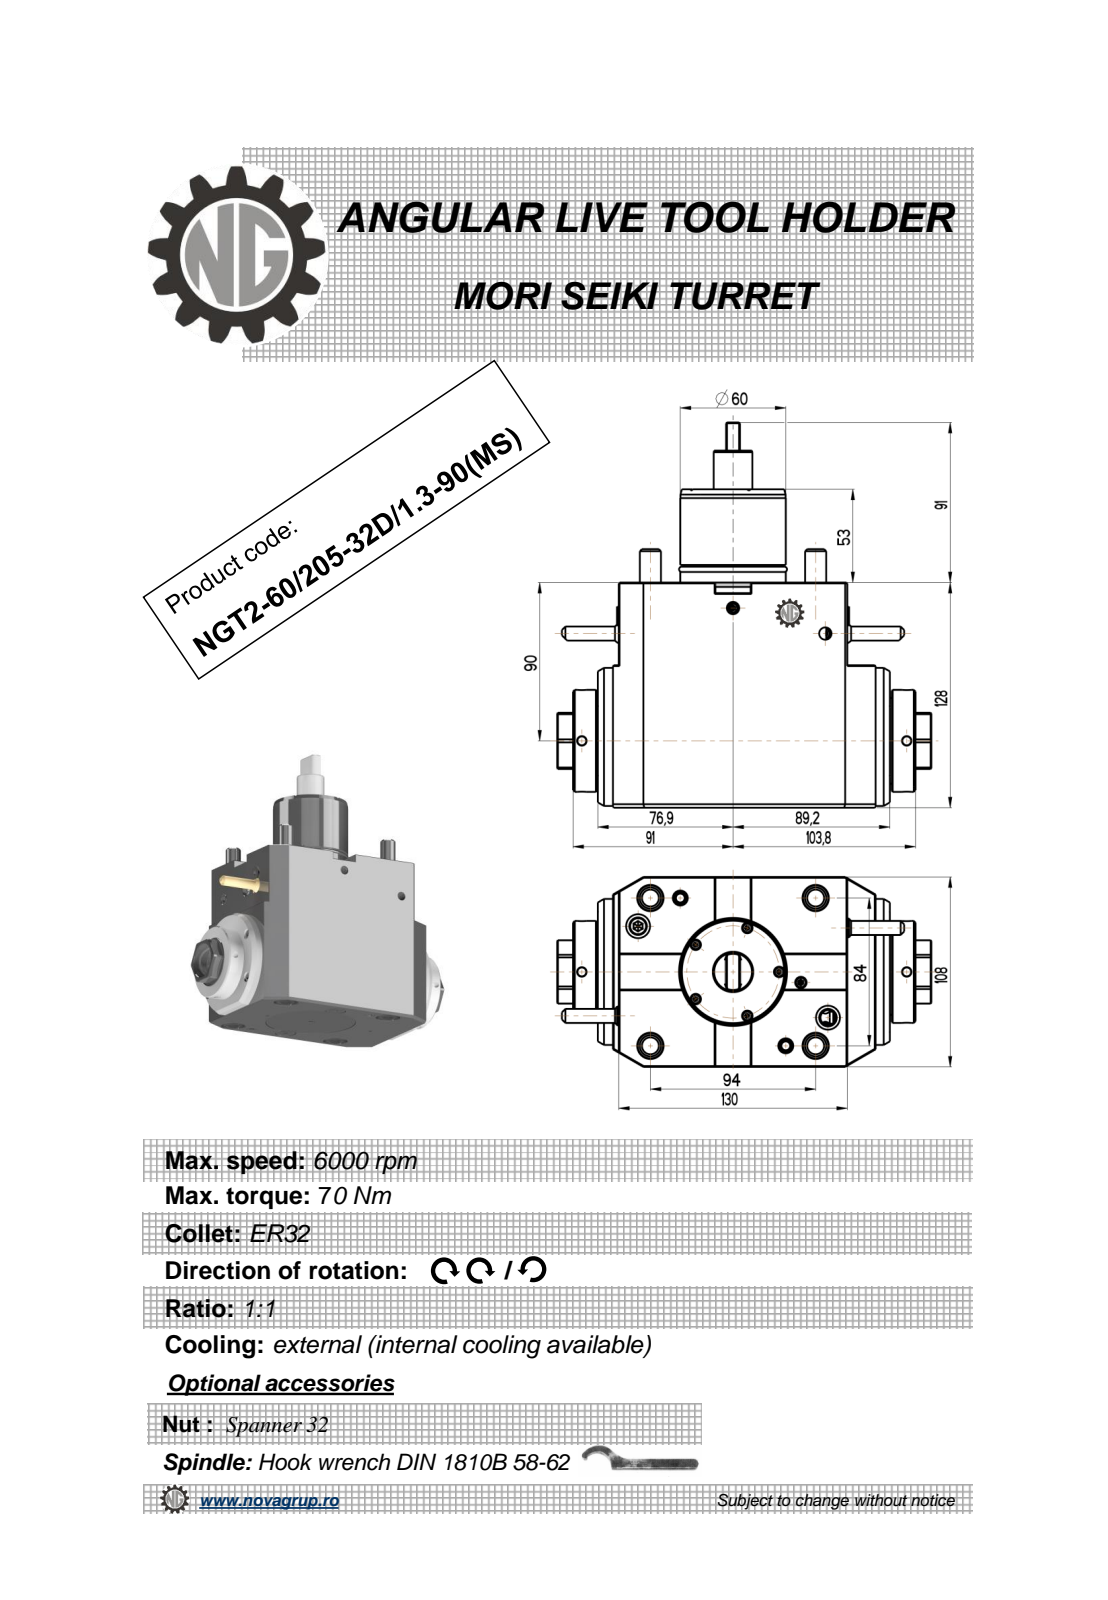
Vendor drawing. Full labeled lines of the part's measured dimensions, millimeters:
Part name (STEP PRODUCT): NGT2_60_201_32D_1_3_90_MS
STEP written by: PRO/ENGINEER BY PARAMETRIC TECHNOLOGY CORPORATION, 2010280 (CONFIG_CONTROL_DESIGN)
Units: millimetres
Bodies: 2 solids, 424 faces (164 planar, 120 cylindrical, 140 other)
Overall size (bounding box): 219 × 212.8 × 109.6
Volume: 2 242 000 mm³ · Surface area: 133 221 mm²
Round holes (diameter × count): ⌀5 ×6, ⌀3 ×2, ⌀13.6 ×2, ⌀8.5 ×1, ⌀27 ×1, ⌀58 ×1
Round bosses / shafts (diameter × count): ⌀12 ×4, ⌀11.2 ×2, ⌀8 ×2, ⌀83 ×1, ⌀60 ×1, ⌀59.8 ×1, ⌀58 ×1, ⌀57.4 ×1
Partial cylindrical surfaces — rounded edges, fillets, slot ends (radius × count): R0.22 ×12, R0.51 ×6, R0.8 ×2, R10.75 ×1, R18 ×1, R39.48 ×1
Main face-to-face distances: 108, 128, 130, 150.9, 6, 53, 22.7, 172.1, 154.2, 24.2
Hole centre spacings: 59.93, 65.92, 184.8, 41.23, 50, 51.8, 86, 98.8
